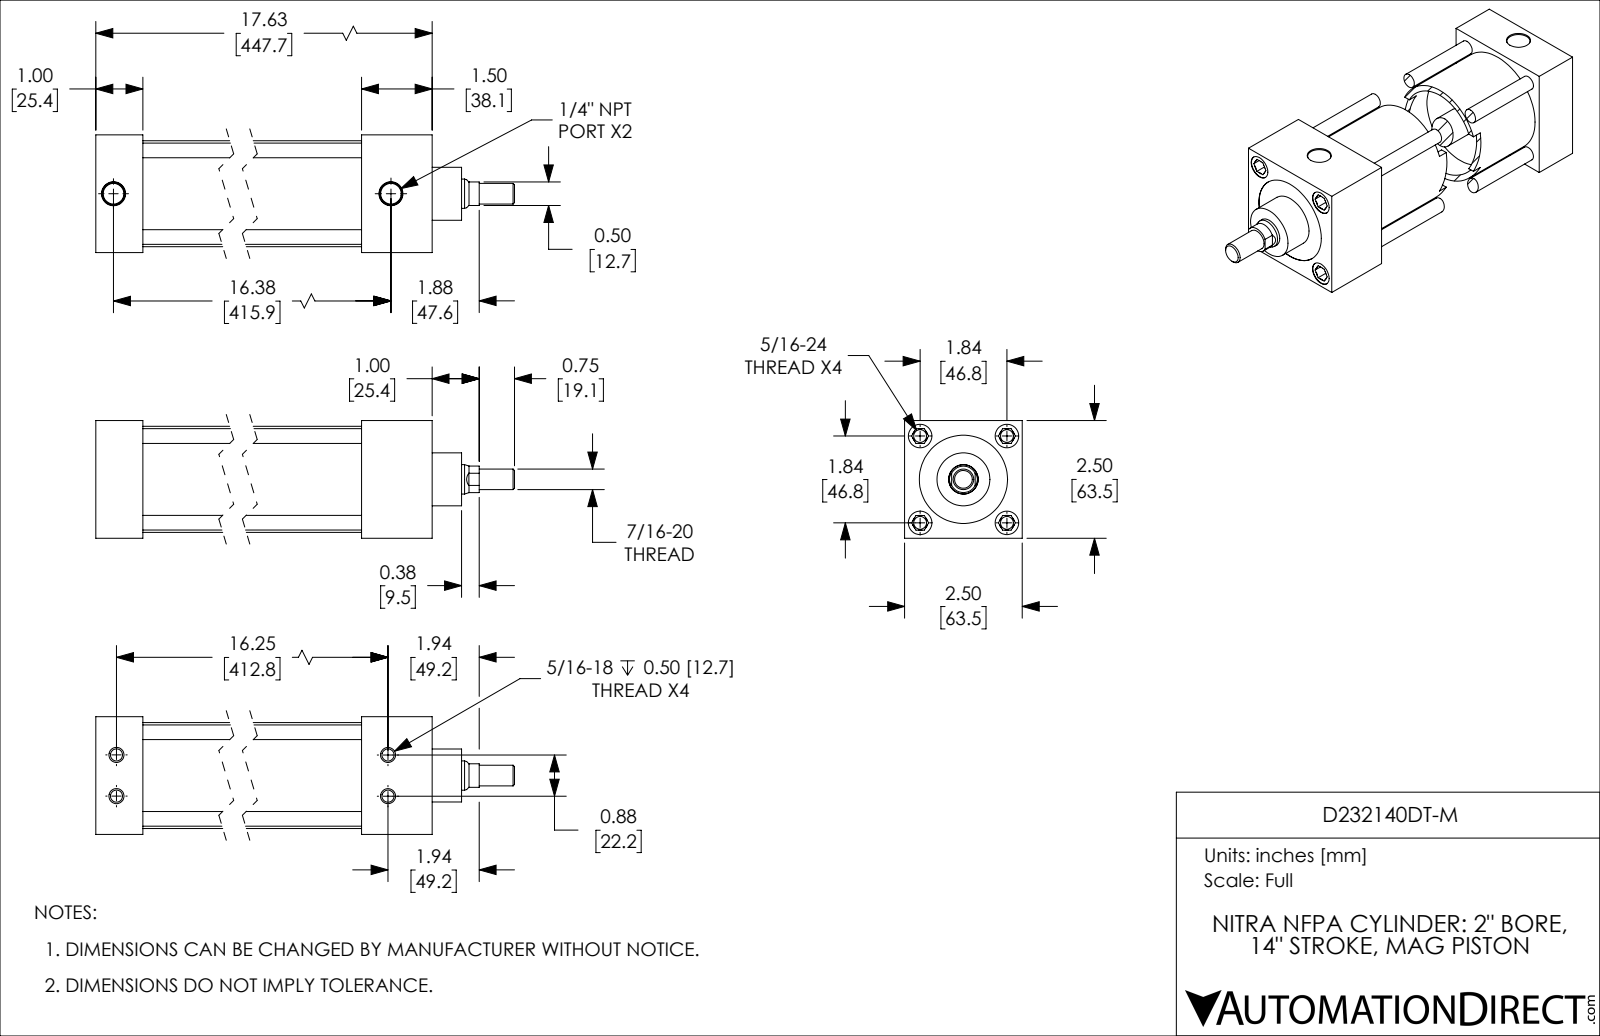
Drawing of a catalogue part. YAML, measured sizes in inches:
part_name: "D232140DT-M_BODY; D232140DT-M; D232140DT-M_PISTON_KK1"
step_written_by: "SolidWorks 2019 (CONFIG_CONTROL_DESIGN)"
units: inches
bodies: {solids: 2, faces: 200, planar: 58, cylindrical: 62, other: 80}
overall_size: [19.375, 2.5, 2.5]
volume: 40.7
surface_area: 371.2
round_holes:
  - {diameter: 0.272, count: 7}
  - {diameter: 0.257, count: 4}
  - {diameter: 0.5, count: 4}
  - {diameter: 0.438, count: 2}
  - {diameter: 0.626, count: 1}
  - {diameter: 1.875, count: 1}
  - {diameter: 2.001, count: 1}
round_bosses_or_shafts:
  - {diameter: 0.312, count: 4}
  - {diameter: 2.251, count: 1}
  - {diameter: 1.999, count: 1}
  - {diameter: 1.125, count: 1}
  - {diameter: 0.624, count: 1}
  - {diameter: 0.437, count: 1}
partial_cylinders:
  - {radius: 0.281, count: 1}
face_to_face_distances: [2.5, 1, 16.125, 15.125, 1.125, 2.125, 14, 1.5, 17.625, 16.625]
hole_center_spacings: [1.84, 1.844, 1.301, 0.441, 0.443, 0.875, 1.304, 2.602]
